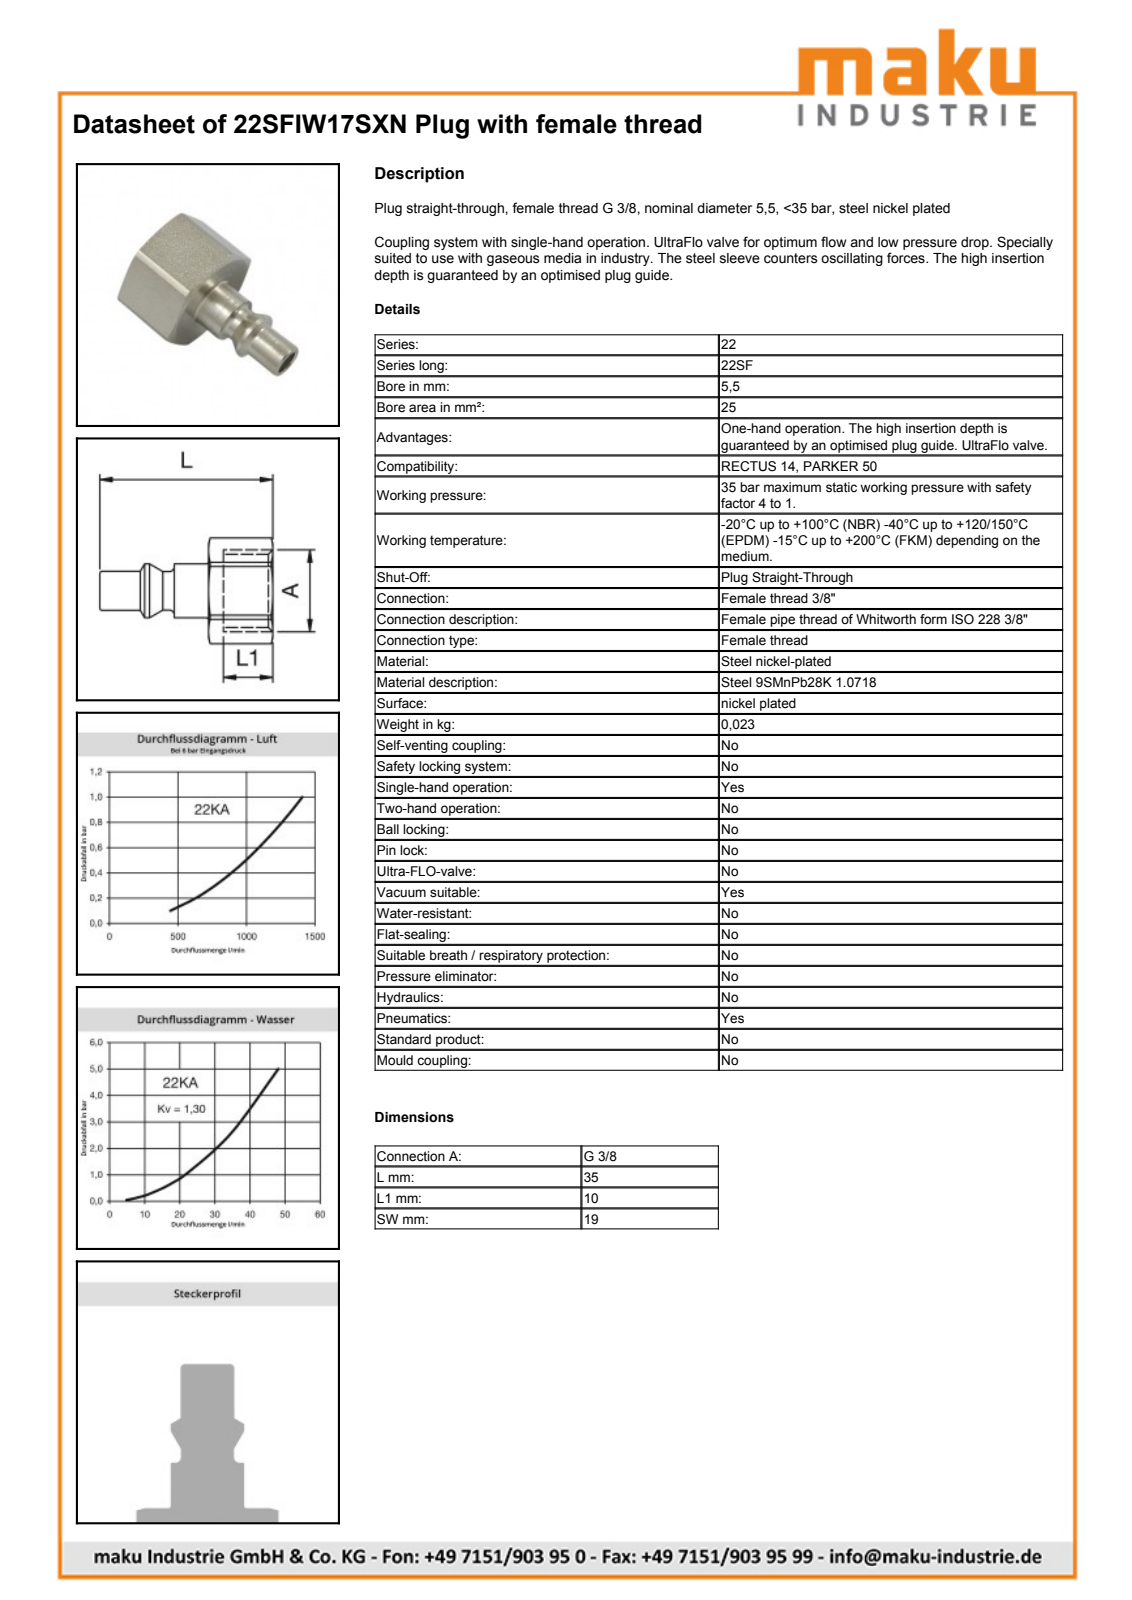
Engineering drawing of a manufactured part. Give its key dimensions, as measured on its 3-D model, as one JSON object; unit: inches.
{"part_name": "D109915", "step_written_by": "Autodesk Inventor 2013 (AUTOMOTIVE_DESIGN)", "units": "inches", "bodies": {"solids": 1, "faces": 41, "planar": 11, "cylindrical": 12, "other": 18}, "overall_size": [1.388, 0.843, 0.748], "volume_in3": 0.174, "surface_area_in2": 4.679, "round_holes": [[0.217, 1], [0.656, 1]], "round_bosses_or_shafts": [[0.429, 1], [0.311, 1], [0.307, 1]], "partial_cylinders_radius": [[0.421, 1]], "face_to_face_distances": [0.748, 0.128, 0.522, 0.394, 0.273, 0.401, 0.794, 0.593, 0.866, 0.994]}
